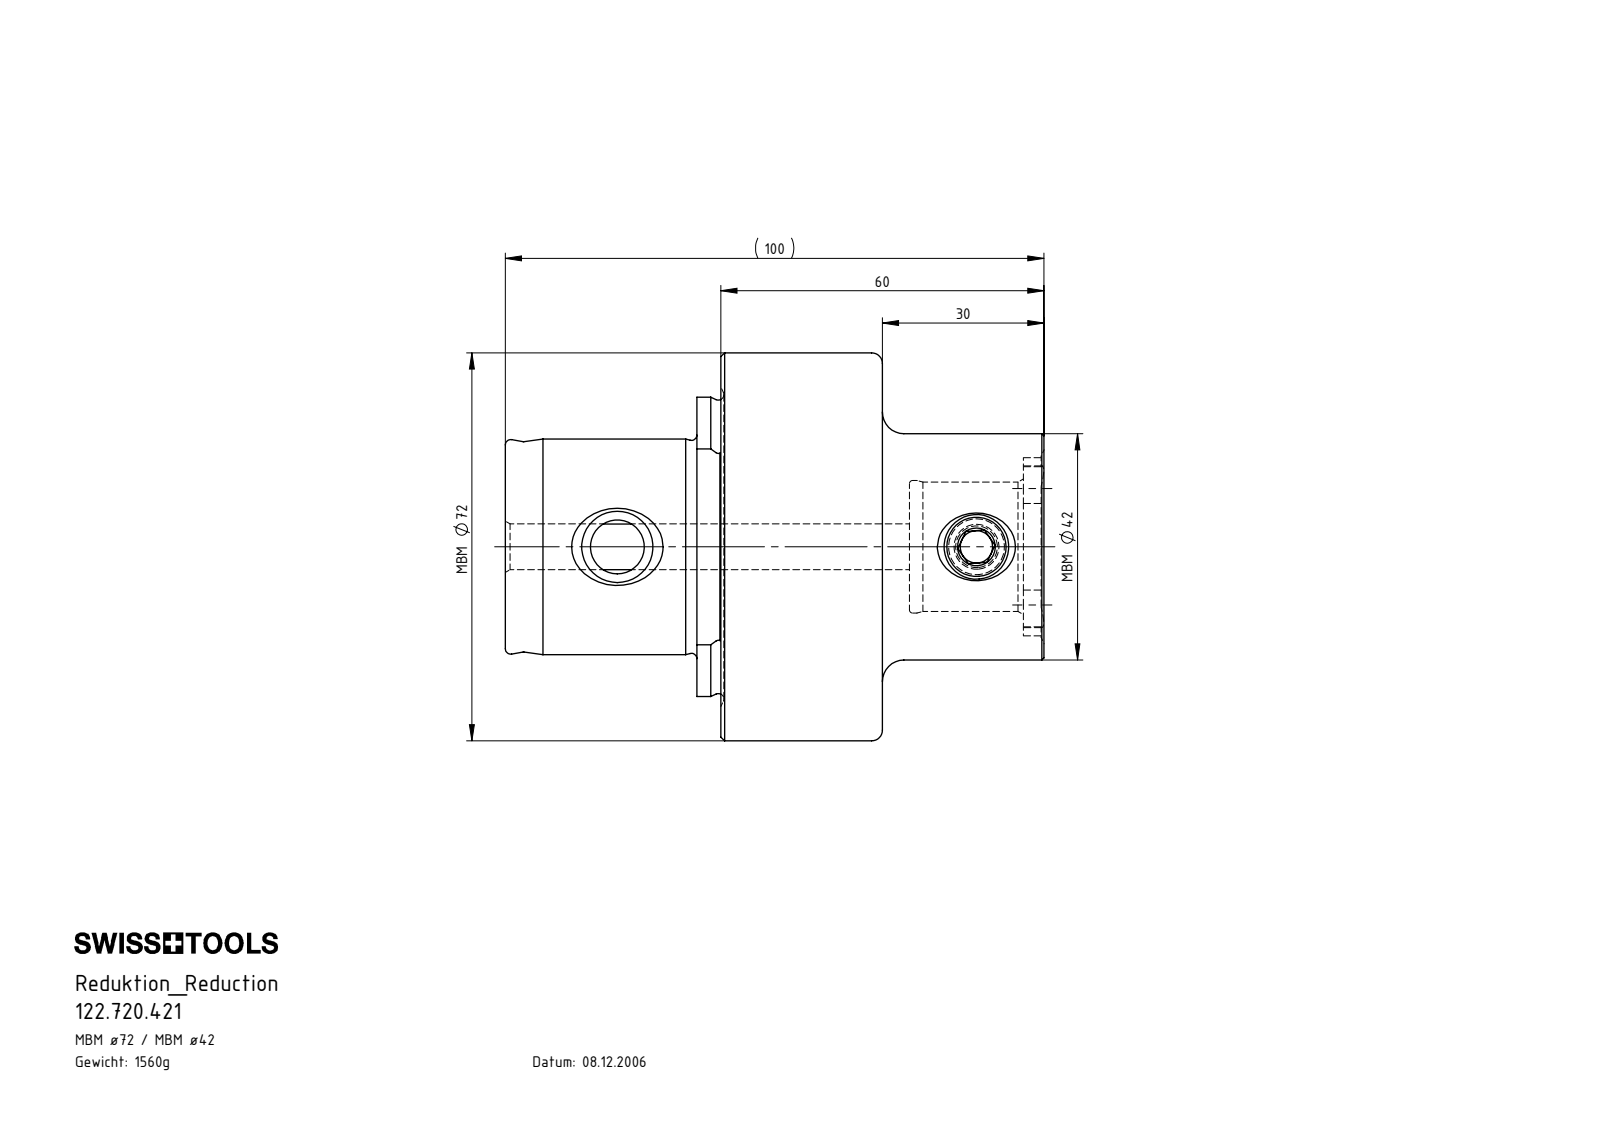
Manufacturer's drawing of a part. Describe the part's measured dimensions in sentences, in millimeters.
The part is named "MB7-MB4.K01.060_C; MB7-MB4.K01.060; MB4-ER1.001.013_A". Its 3-D file was written by "SolidWorks 2017 (AUTOMOTIVE_DESIGN)". It is 2 solids with 135 faces: 35 planar, 35 cylindrical and 65 other. Overall it measures 100 by 72 by 72 millimeters. Its volume is 198 778 cubic millimeters and its surface area 28 576 square millimeters. Round holes: 1 of diameter 6, 1 of diameter 8.5, 1 of diameter 10, 1 of diameter 11, 1 of diameter 24, 1 of diameter 24.6. Round bosses or shafts: 1 of diameter 72, 1 of diameter 42, 1 of diameter 40, 1 of diameter 12. Partial cylindrical surfaces (rounded edges, fillets, slot ends): 4 of radius 4.2, 1 of radius 14.9, 1 of radius 16.52, 1 of radius 27.77. The main face-to-face distances are 30, 40, 70, 35.55, 4.45, 34.45, 75, 39.45, 35, 5. The hole center spacings are 66.65.
